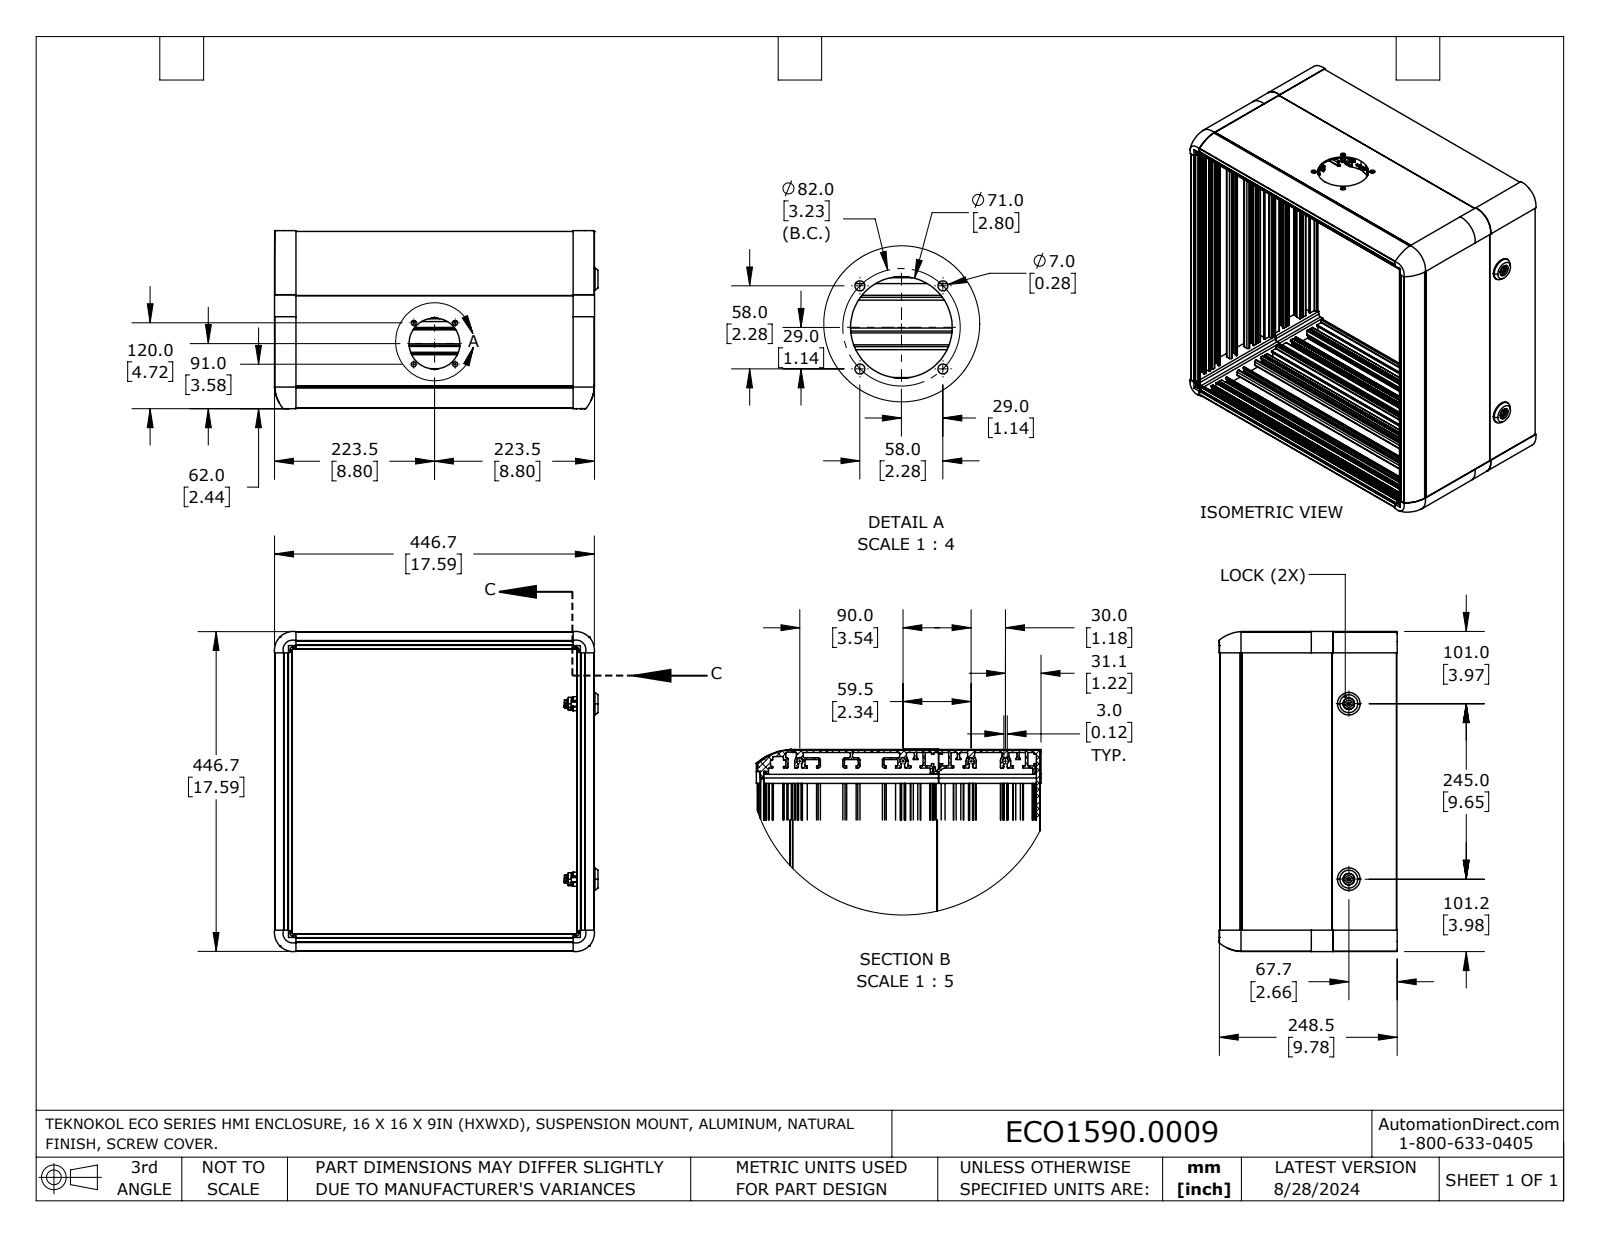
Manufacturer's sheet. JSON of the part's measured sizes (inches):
{"part_name": "ECO.1590.0009(400x400)", "step_written_by": "SolidWorks 2023 (AUTOMOTIVE_DESIGN)", "units": "inches", "bodies": {"solids": 34, "faces": 3184, "planar": 1634, "cylindrical": 1174, "other": 376}, "overall_size": [17.79, 17.604, 9.788], "volume_in3": 209.4, "surface_area_in2": 3648, "round_holes": [[0.256, 8], [0.205, 4], [0.276, 4], [0.197, 2], [0.236, 2], [0.237, 2], [0.394, 2], [0.478, 2], [0.63, 2], [2.795, 1]], "round_bosses_or_shafts": [[0.374, 4], [1.24, 2], [0.624, 2], [0.583, 2], [0.531, 2], [0.51, 2], [0.508, 2], [0.386, 2]], "partial_cylinders_radius": [[0.02, 404], [0.039, 86], [0.079, 66], [0.008, 48], [0.014, 40], [0.01, 24], [0.016, 20], [0.177, 20]], "face_to_face_distances": [17.453, 0.089, 0.118, 17.542, 17.365, 0.079, 0.62, 16.922, 0.531, 16.833], "hole_center_spacings": [0.666, 1.181, 1.615, 1.754, 2.283, 9.646, 1.344, 2.343]}
